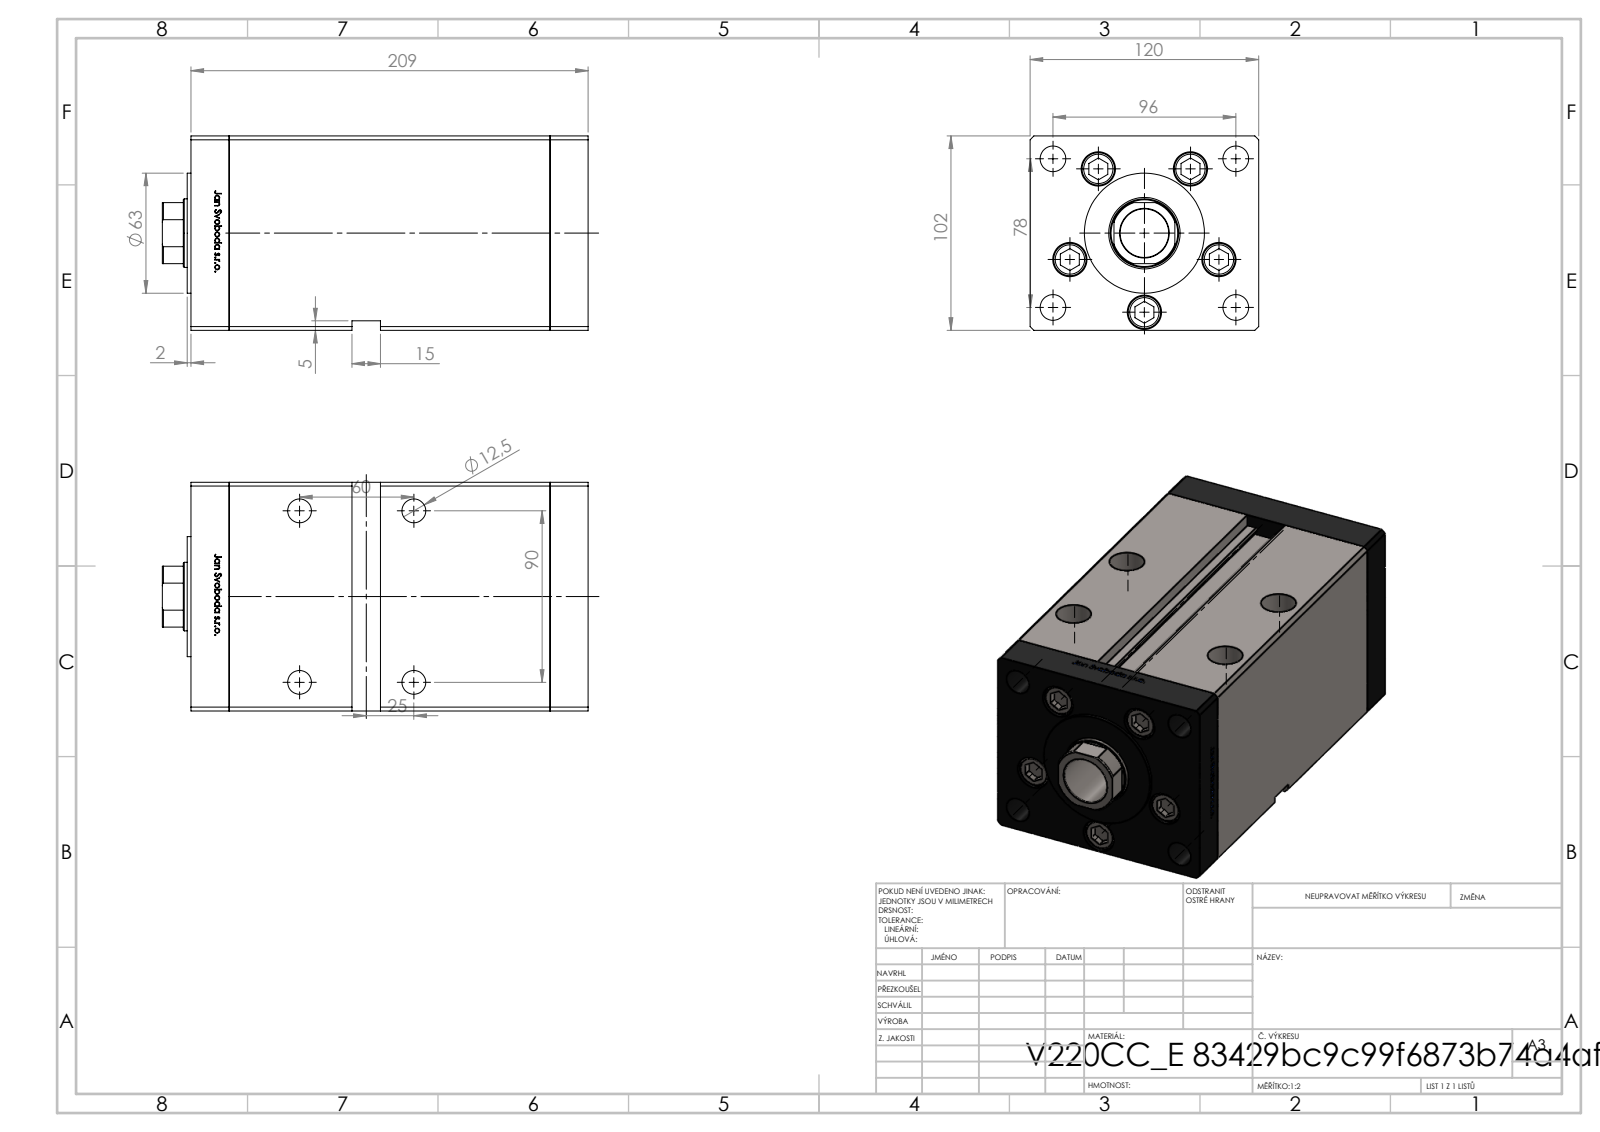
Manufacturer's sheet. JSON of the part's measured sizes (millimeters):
{"part_name": "V220C_FRONT_E; V220C_VC_E; ALLEN BOLT; V220C BACK_E (+1 more)", "step_written_by": "SolidWorks 2019 (CONFIG_CONTROL_DESIGN)", "units": "millimeters", "bodies": {"solids": 14, "faces": 1214, "planar": 475, "cylindrical": 165, "other": 574}, "overall_size": [223.5, 120, 102], "volume_mm3": 2171000, "surface_area_mm2": 289843, "round_holes": [[13.5, 9], [18, 5], [12.5, 4], [18.5, 4], [2, 2], [13.16, 2], [25.5, 1], [36, 1], [37.5, 1]], "round_bosses_or_shafts": [[17, 5], [8, 5], [63, 1]], "partial_cylinders_radius": [[0.93, 2], [17.5, 1]], "face_to_face_distances": [120, 20, 102, 168.5, 188.5, 34.25, 208.5, 14.25, 154.25, 174.25], "hole_center_spacings": [41.5, 61.85, 24.39, 26.69, 47.92, 48.07, 49.84, 53.57]}
